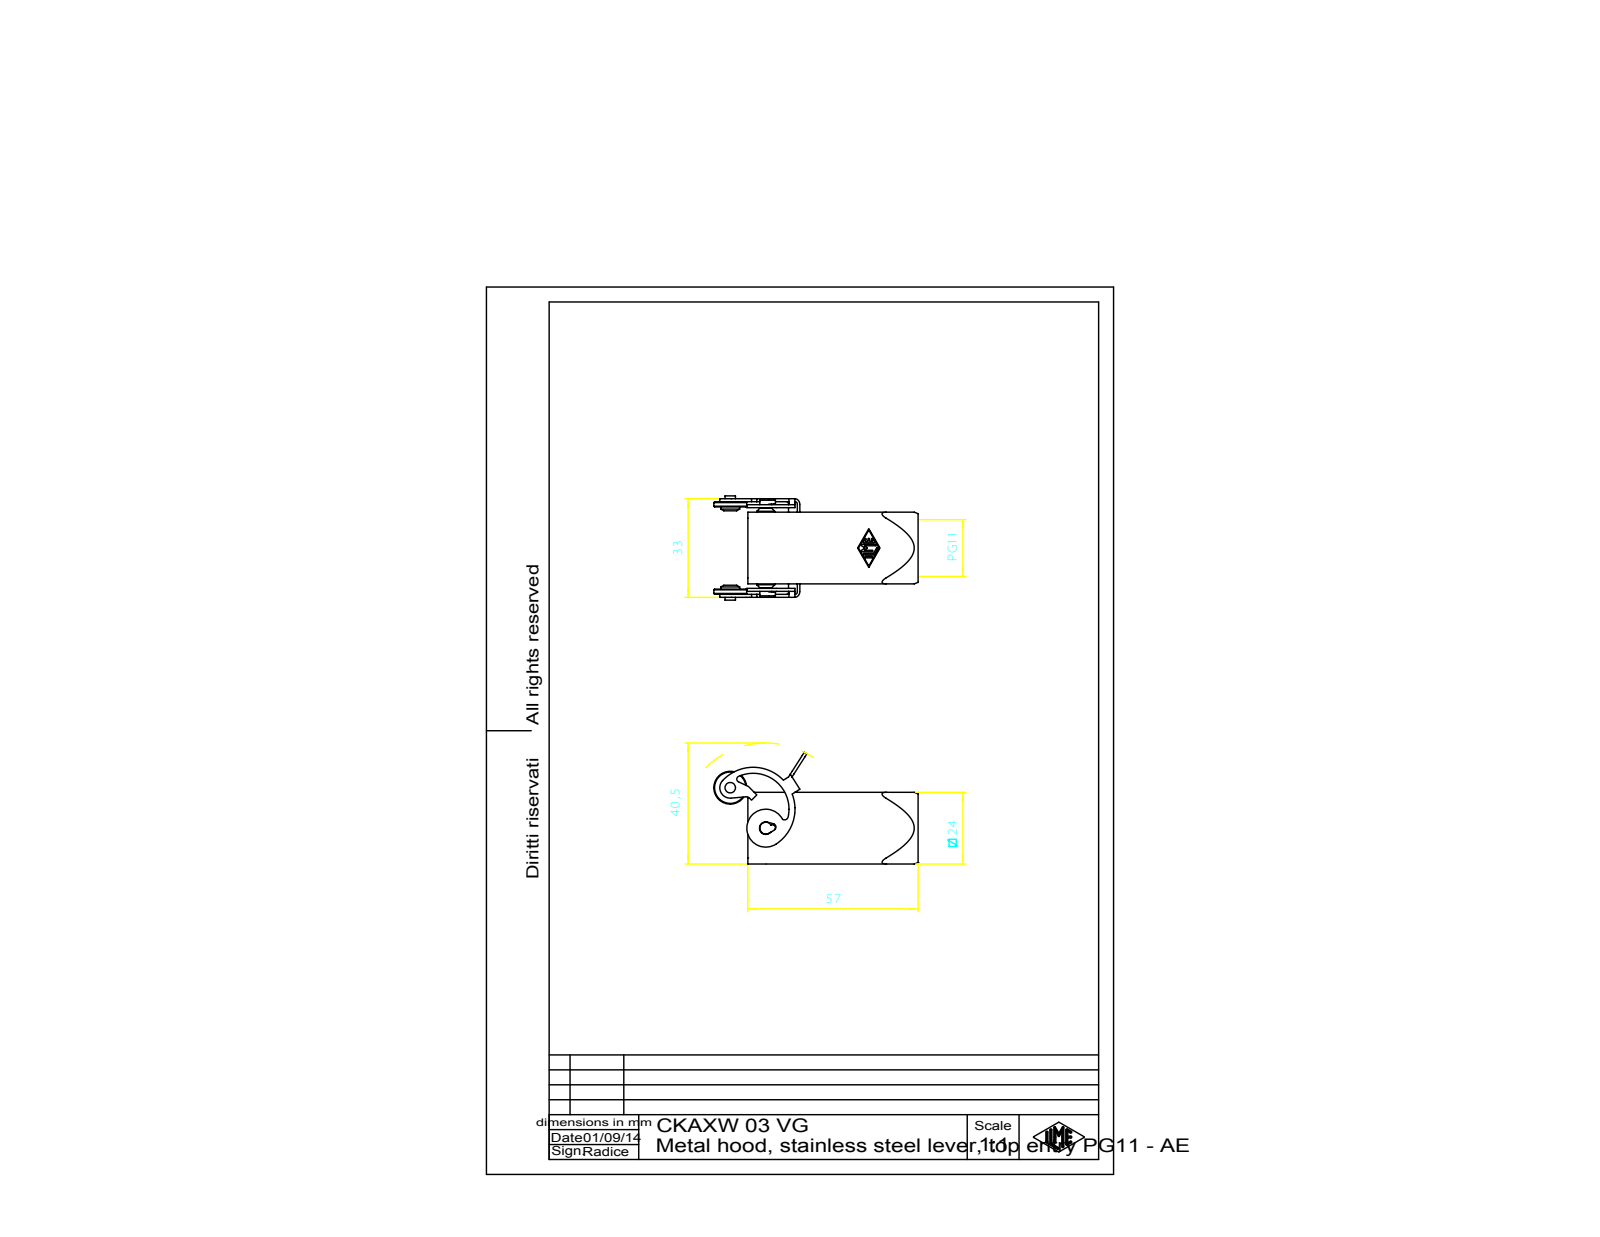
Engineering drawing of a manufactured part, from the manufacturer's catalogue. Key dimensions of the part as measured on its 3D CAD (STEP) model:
Part name (STEP PRODUCT): CKAXW 03 VG
STEP written by: Autodesk Inventor 7 (AUTOMOTIVE_DESIGN)
Units: millimetres
Bodies: 2 solids, 237 faces (81 planar, 90 cylindrical, 66 other)
Overall size (bounding box): 62.9 × 37.42 × 34.9
Volume: 8 845 mm³ · Surface area: 12 105 mm²
Round holes (diameter × count): ⌀3.3 ×1, ⌀15 ×1, ⌀17.26 ×1
Round bosses / shafts (diameter × count): ⌀11 ×1, ⌀6.3 ×1, ⌀6 ×1, ⌀4 ×1, ⌀3.5 ×1
Partial cylindrical surfaces — rounded edges, fillets, slot ends (radius × count): R2 ×18, R0.25 ×14, R1 ×6, R0.8 ×2, R1.1 ×1, R1.25 ×1, R1.5 ×1, R2.1 ×1
Main face-to-face distances: 1, 23, 24, 22, 2, 3, 2.5, 25.5, 3.5, 26.5
